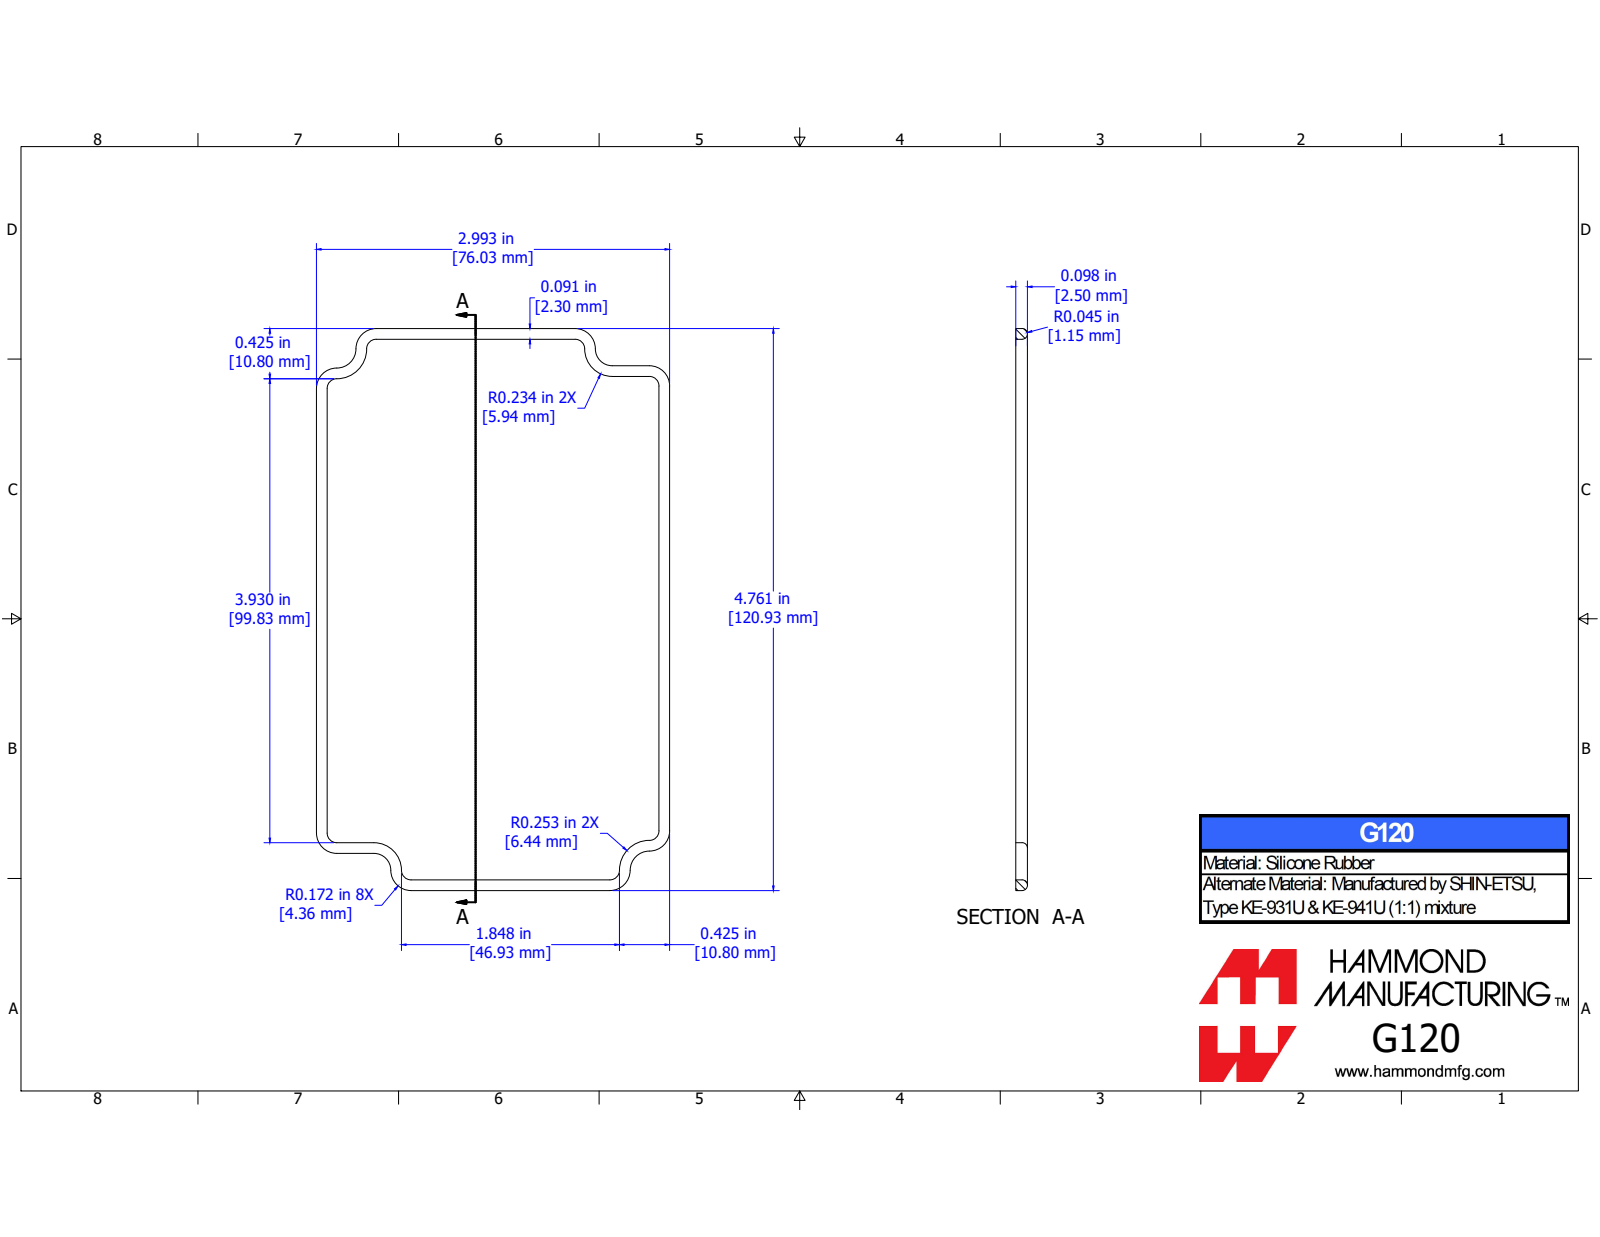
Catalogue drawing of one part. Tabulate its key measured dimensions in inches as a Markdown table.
| quantity | value |
| --- | --- |
| part name | 1590Z120G |
| STEP written by | SolidWorks 2019 (CONFIG_CONTROL_DESIGN) |
| units | inches |
| bodies | 1 solid, 158 faces (40 planar, 24 cylindrical, 94 other) |
| overall size | 4.78 × 3.008 × 0.093 |
| volume | 0.116 in³ |
| surface area | 4.956 in² |
| partial cylindrical surfaces (radius × count) | 0.039 × 20 |
| main face-to-face distances | 2.894, 0.091, 4.659, 0.318, 4.341, 4.023, 0.093, 0.631, 2.263, 2.576 |
